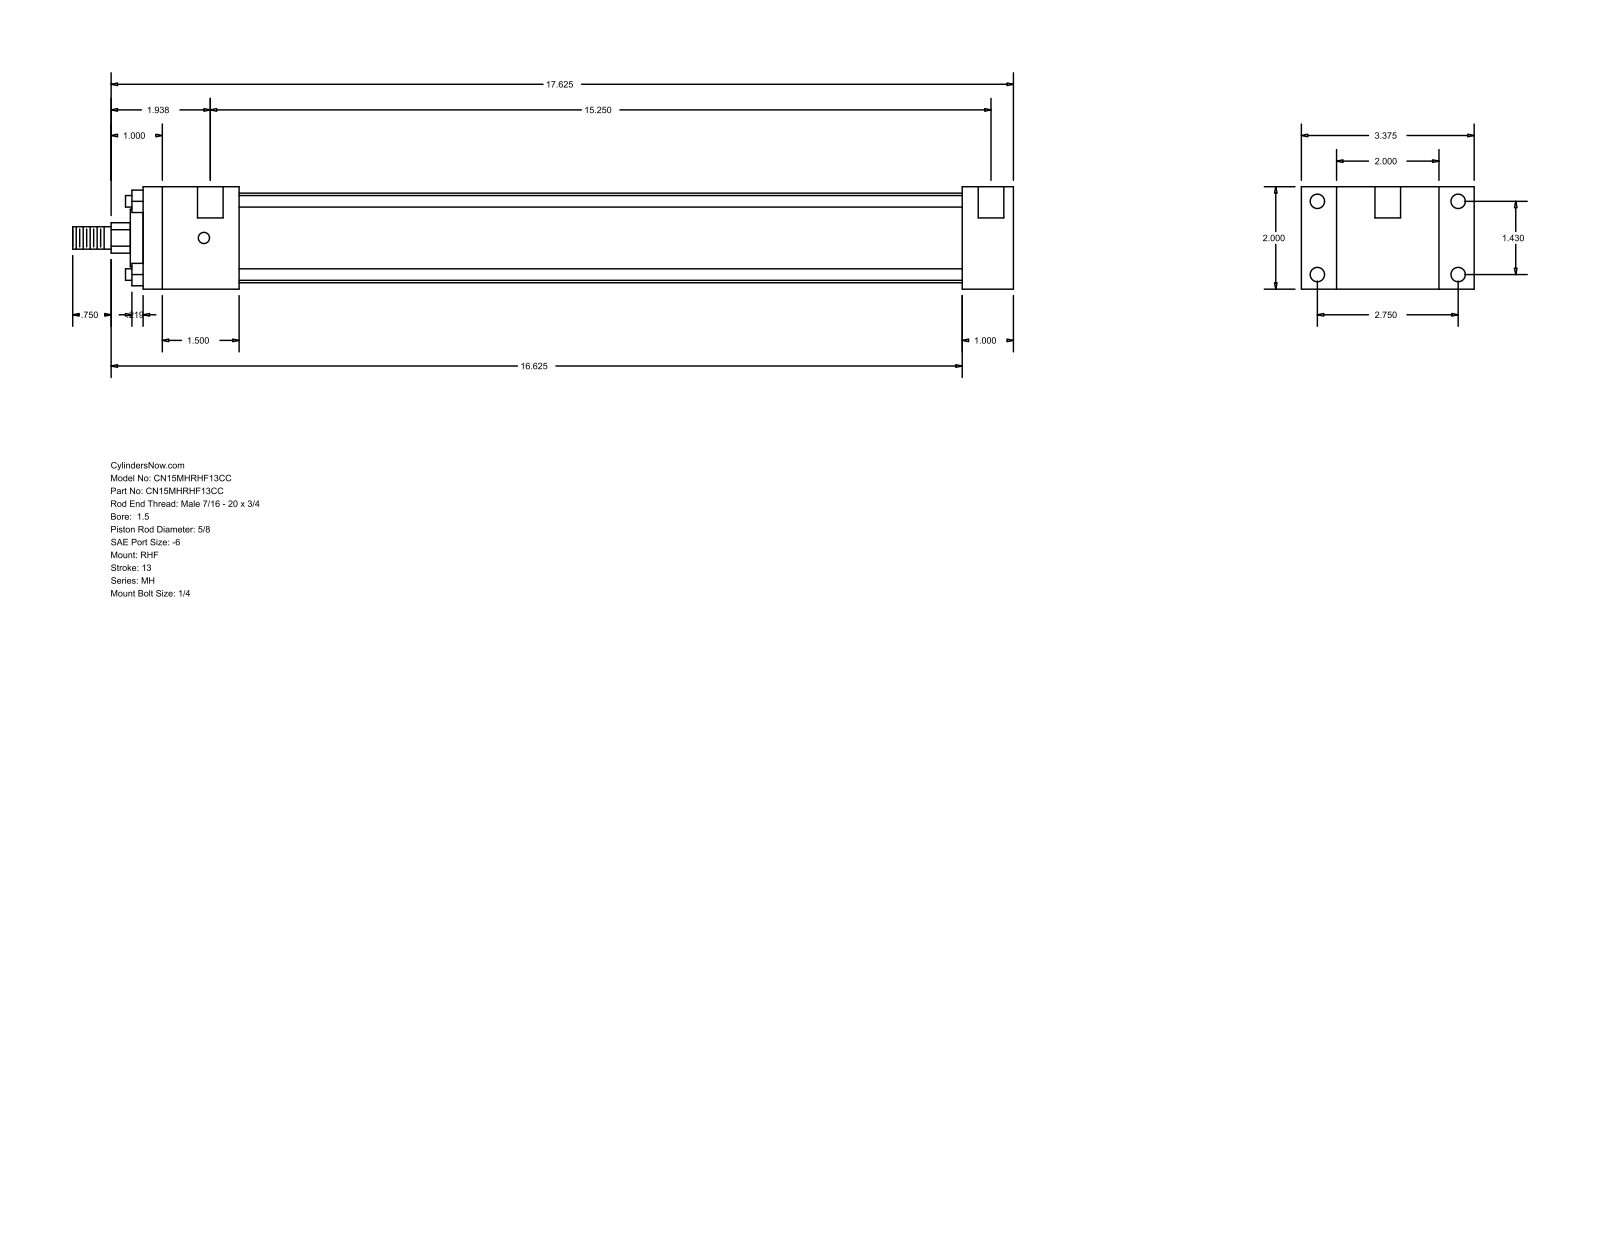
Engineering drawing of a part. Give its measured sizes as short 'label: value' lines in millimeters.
name: MH_RHF__0150_0.625
written by: GSSL Pune (CONFIG_CONTROL_DESIGN)
unit: mm
bodies: 0 solids, 88 faces (60 planar, 28 cylindrical, 0 other)
size: 466.73 × 85.72 × 50.8
holes: 4× ⌀5.56, 4× ⌀7.14, 2× ⌀12.7
bosses: 4× ⌀5.71, 1× ⌀44.45, 1× ⌀28.57, 1× ⌀15.88, 1× ⌀11.11
rounds: 1× R7.54
face distances: 50.8, 17.46, 68.26, 25.41, 406.39, 431.8, 85.72, 47.62, 358.77, 384.18
hole spacings: 36.32, 69.84, 78.72, 390.52, 3.17, 387.35
